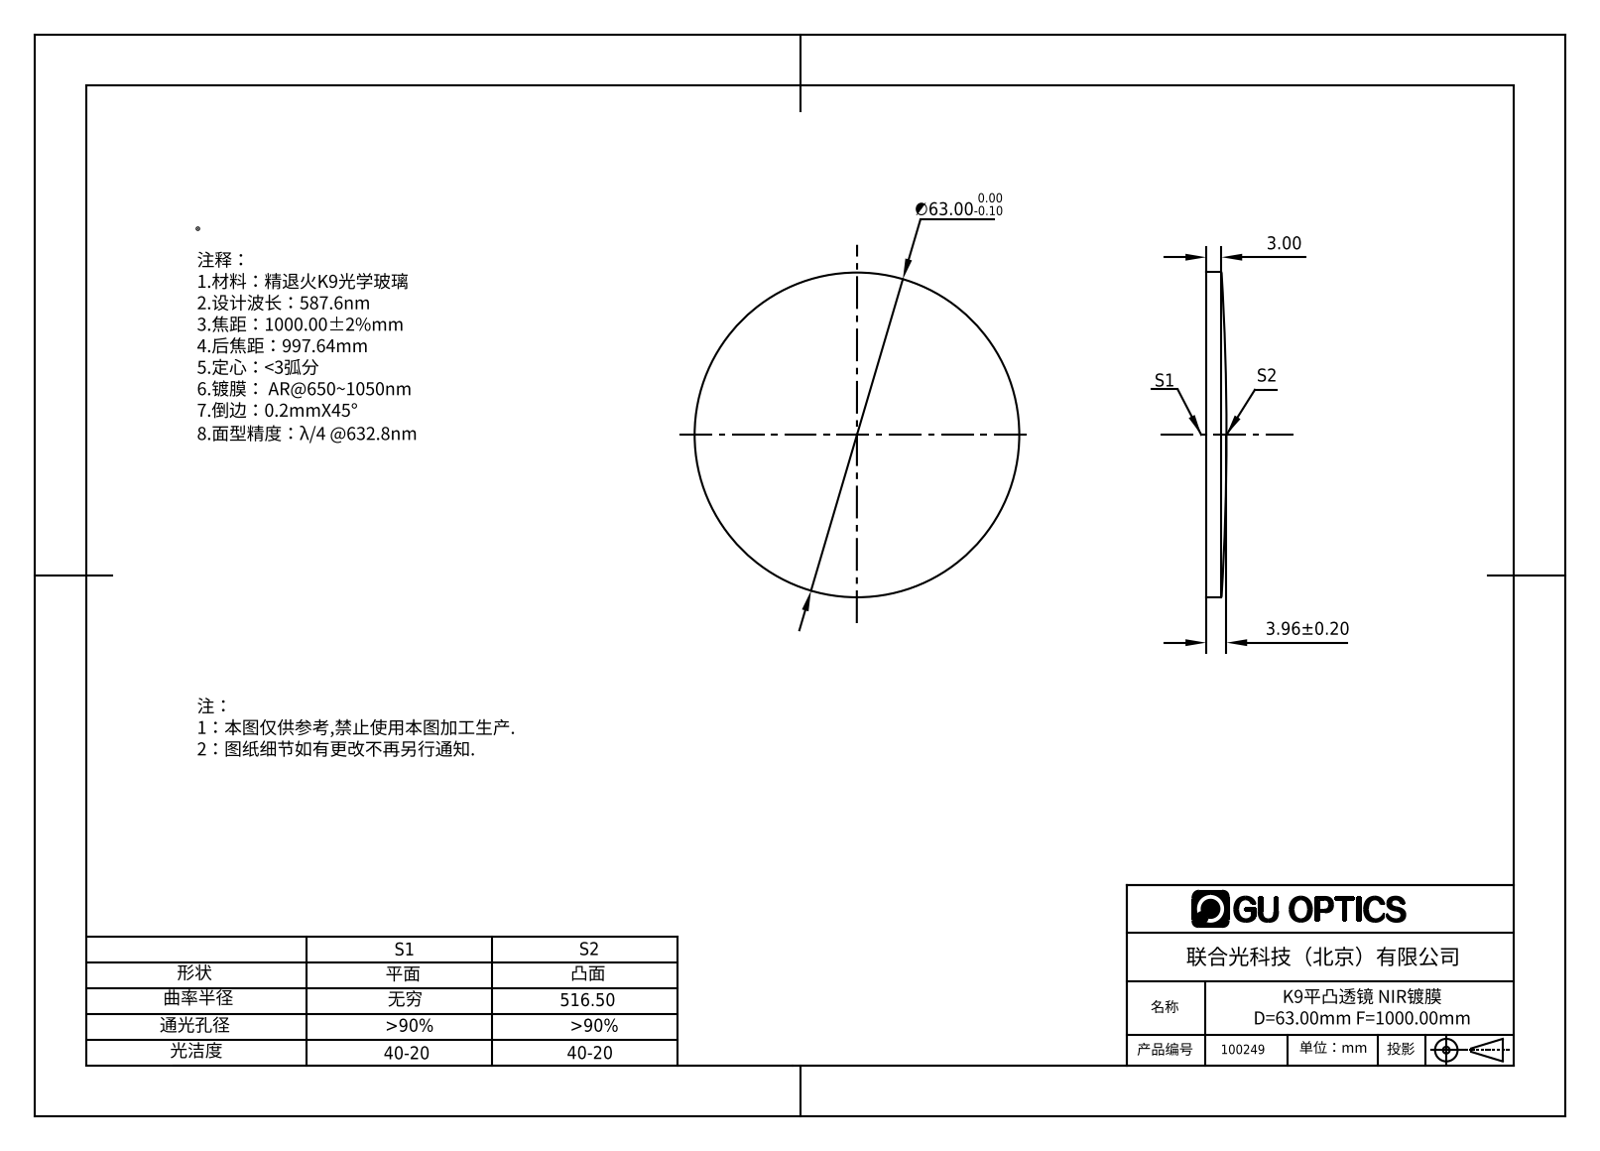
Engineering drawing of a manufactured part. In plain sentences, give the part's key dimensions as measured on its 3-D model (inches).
The part is named "100249". Its 3-D file was written by "SolidWorks 2016 (AUTOMOTIVE_DESIGN)". It is 1 solid with 5 faces: 1 planar, 2 cylindrical and 2 other. Overall it measures 2.48 by 2.48 by 0.156 inches. Its volume is 0.662 cubic inches and its surface area 10.59 square inches. Round bosses or shafts: 1 of diameter 2.48.
